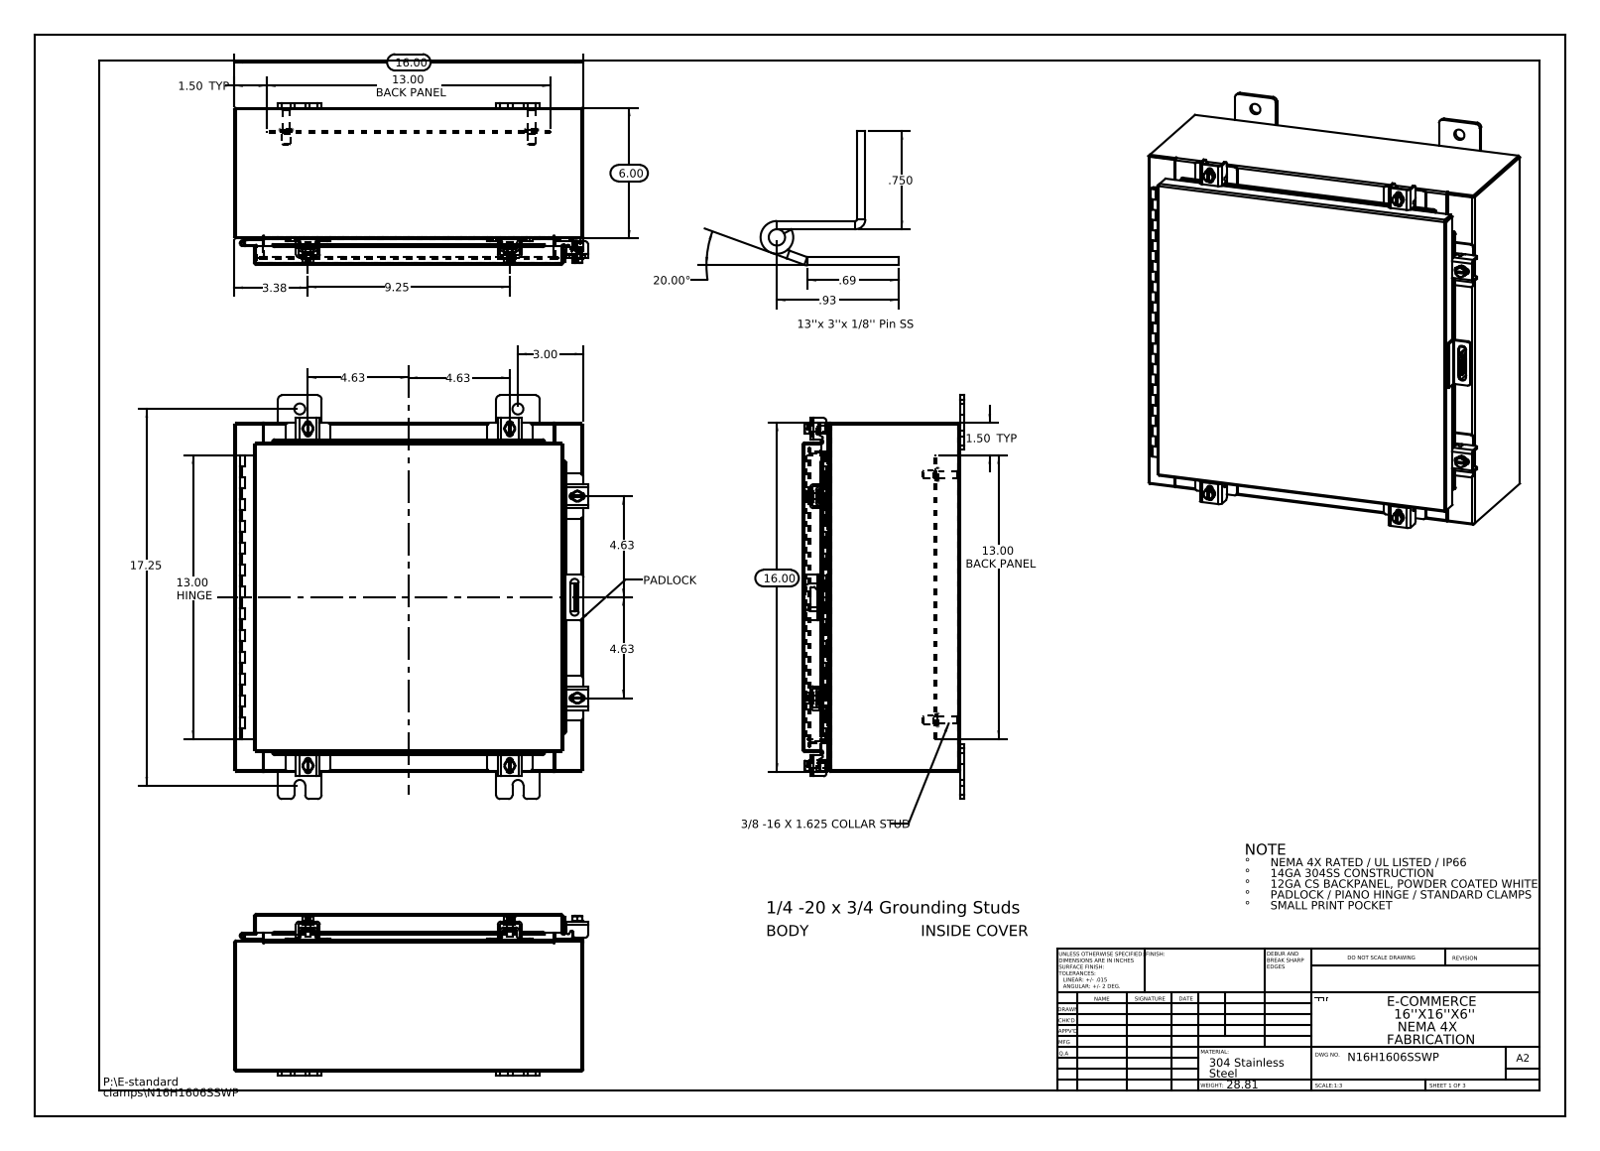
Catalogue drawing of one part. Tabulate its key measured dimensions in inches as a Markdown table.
| quantity | value |
| --- | --- |
| part name | N16H1606SSWP 22104005_DEFAULT; N16H1606SSWP Padlock Hasp; N16H1606SSWP Hinge Cover Side; N16H1606SSWP (+8 more) |
| STEP written by | SolidWorks 2013 (CONFIG_CONTROL_DESIGN) |
| units | inches |
| bodies | 47 solids, 1501 faces (800 planar, 605 cylindrical, 96 other) |
| overall size | 18.5 × 16.211 × 7.389 |
| volume | 102.2 in³ |
| surface area | 2 591 in² |
| round holes (diameter × count) | 0.5 × 8, 0.213 × 6, 0.26 × 6, 0.125 × 2, 0.125 × 1 |
| round bosses / shafts (diameter × count) | 0.25 × 7, 0.5 × 6, 0.399 × 6, 0.625 × 4, 0.375 × 4, 0.33 × 4 |
| partial cylindrical surfaces (radius × count) | 0.06 × 30, 0.19 × 24, 0.013 × 23, 0.088 × 21, 0.12 × 12, 0.141 × 12, 0.125 × 10, 0.05 × 9 |
| main face-to-face distances | 0.075, 7.126, 15.925, 7.201, 7.051, 15.85, 16, 1, 1.075, 6.051 |
| hole center spacings | 13.388, 10.463, 16.832, 1.858, 2.326, 2.326, 2.327, 3.065 |
